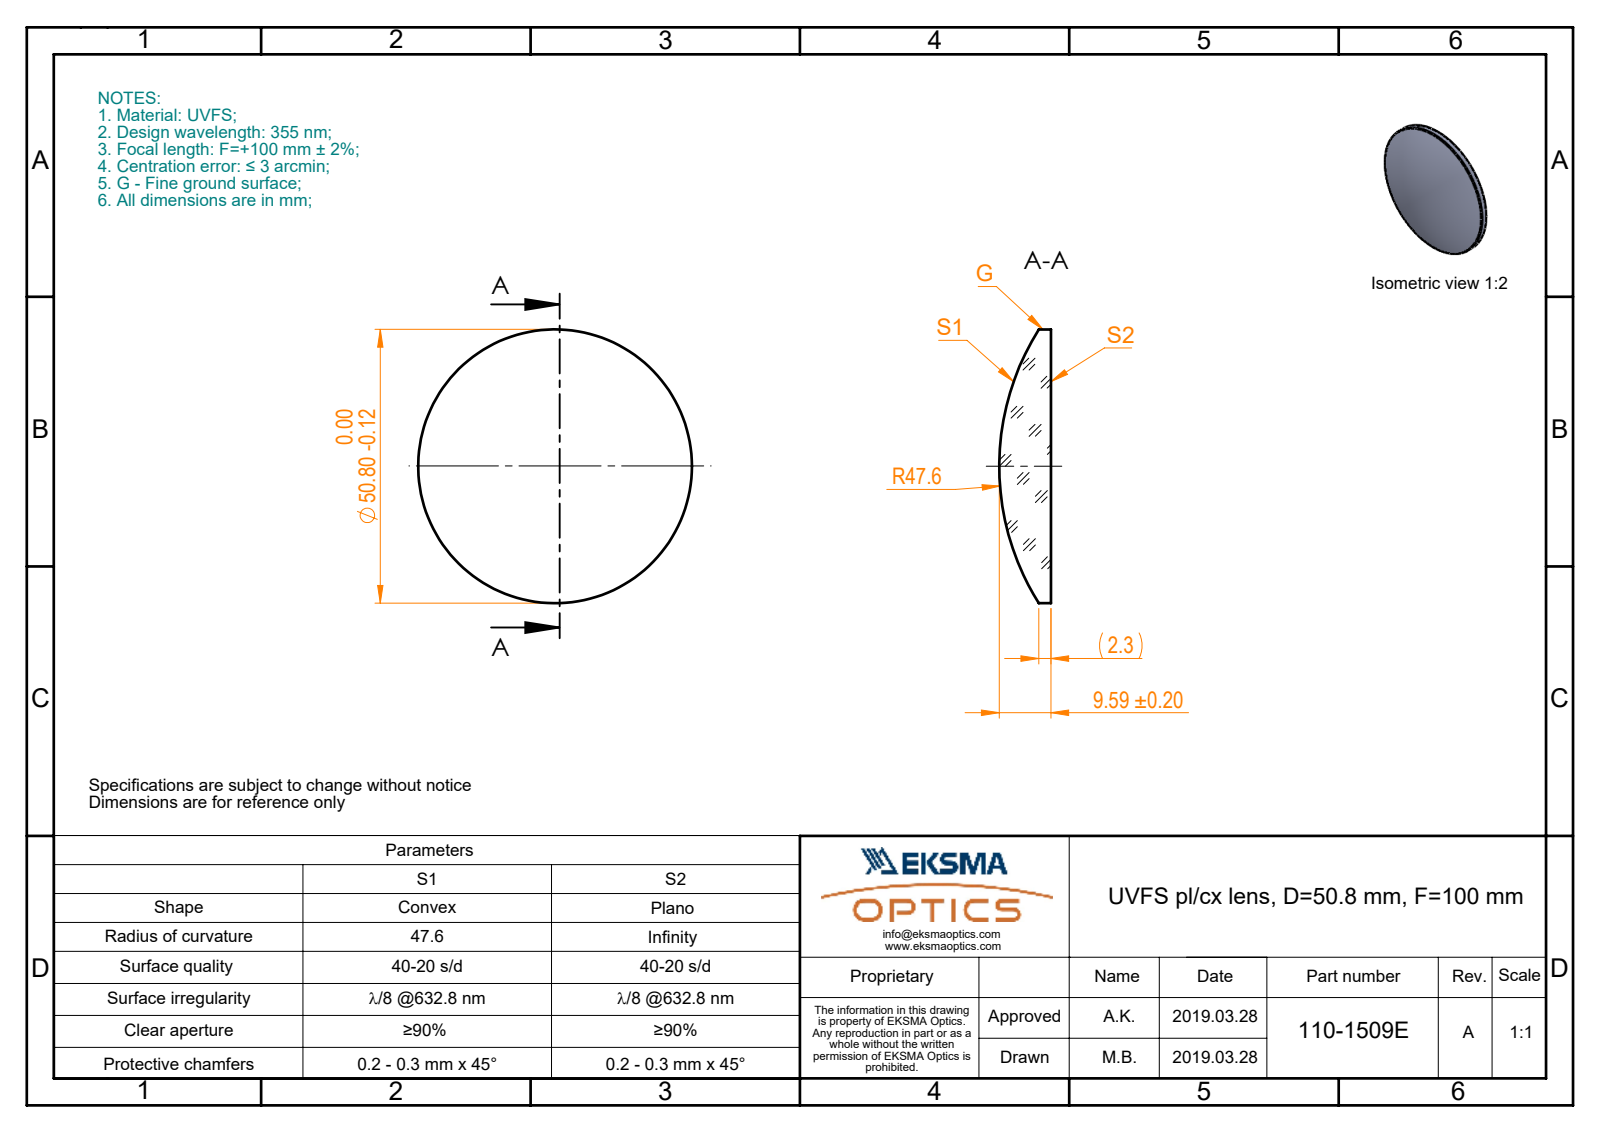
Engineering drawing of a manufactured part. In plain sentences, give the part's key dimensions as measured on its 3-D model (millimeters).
The part is named "110-1509E UVFS pl-cx 50.8 F100". Its 3-D file was written by "SolidWorks 2017 (CONFIG_CONTROL_DESIGN)". It is 1 solid with 5 faces: 1 planar, 2 cylindrical and 2 other. Overall it measures 50.8 by 50.8 by 9.6 millimeters. Its volume is 12 225 cubic millimeters and its surface area 4 583 square millimeters. Round bosses or shafts: 1 of diameter 50.8.
